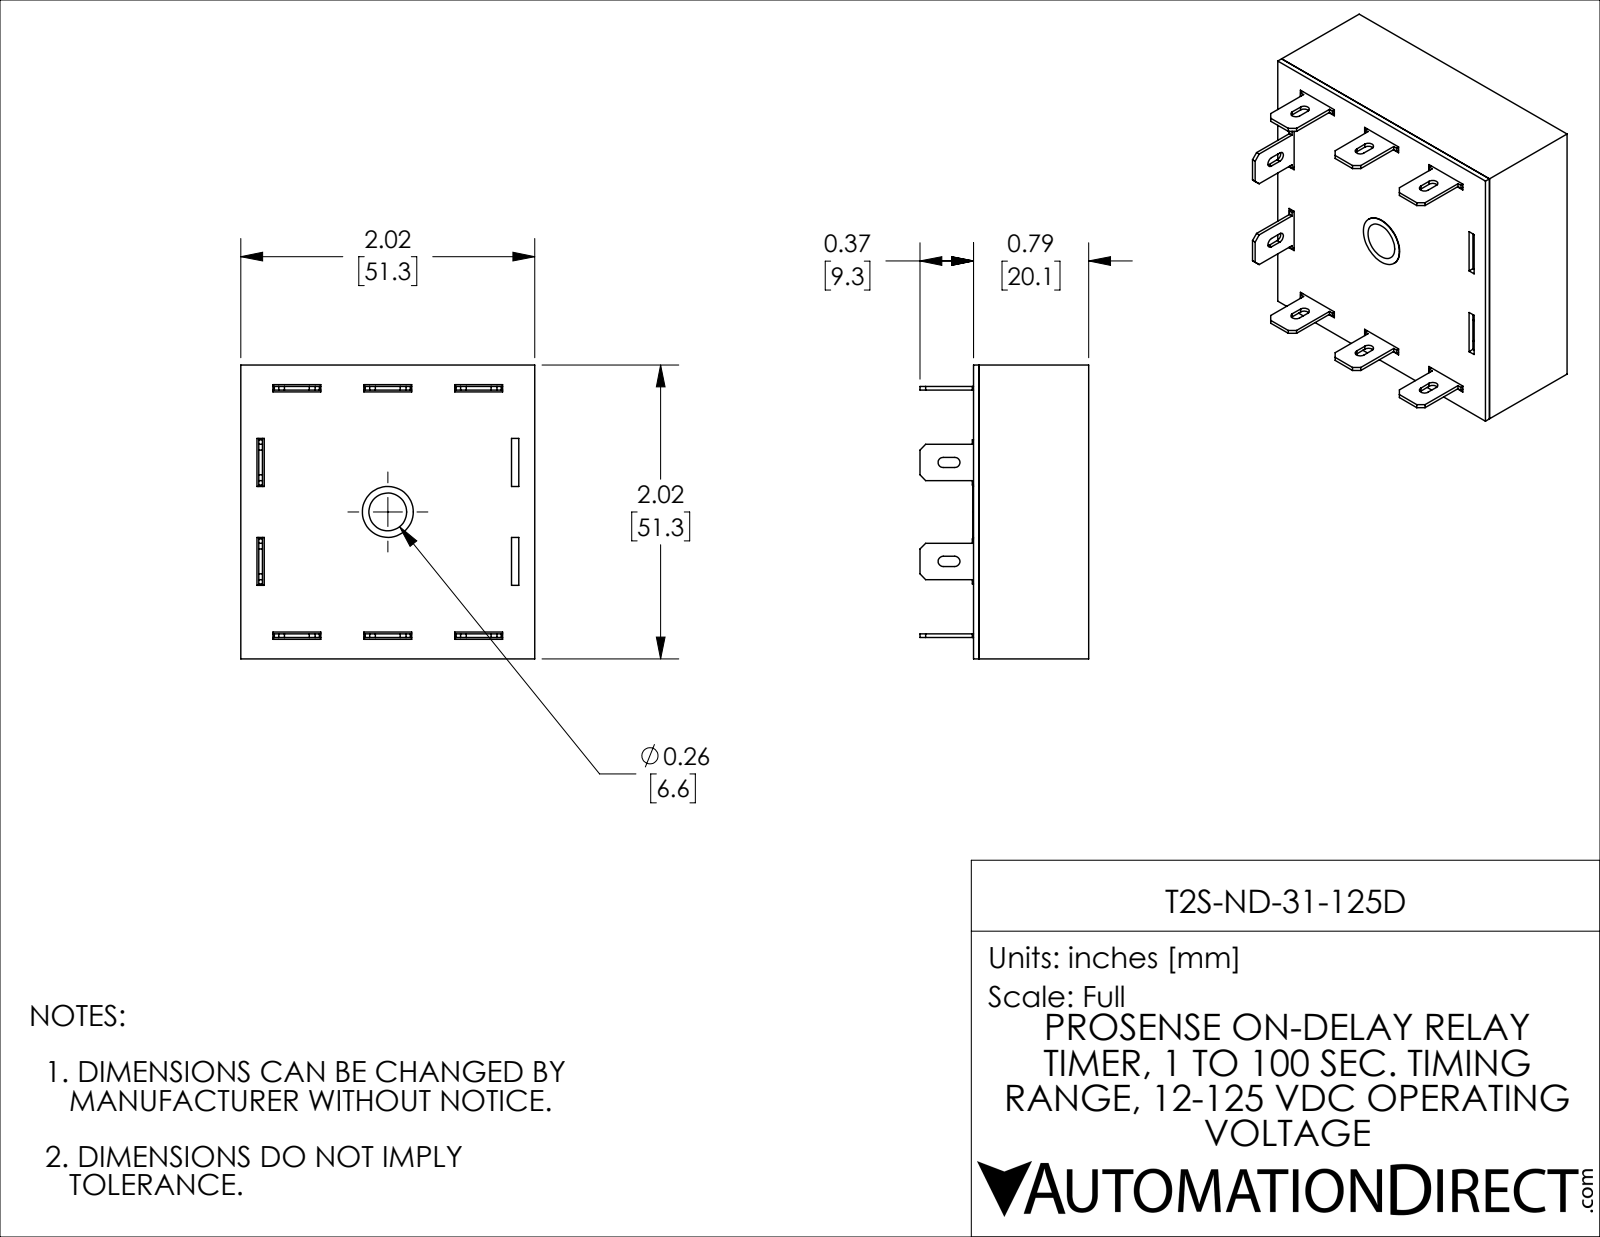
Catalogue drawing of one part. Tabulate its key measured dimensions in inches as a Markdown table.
| quantity | value |
| --- | --- |
| part name | T2S-ND-31-125D |
| STEP written by | SolidWorks 2021 (CONFIG_CONTROL_DESIGN) |
| units | inches |
| bodies | 10 solids, 256 faces (234 planar, 20 cylindrical, 2 other) |
| overall size | 2.02 × 2.02 × 1.16 |
| volume | 0.674 in³ |
| surface area | 35.37 in² |
| round holes (diameter × count) | 0.35 × 1 |
| partial cylindrical surfaces (radius × count) | 0.035 × 10 |
| main face-to-face distances | 0.045, 1.975, 0.754, 0.792, 0.038, 0.709, 0.747, 2.02, 1.93, 0.147 |
